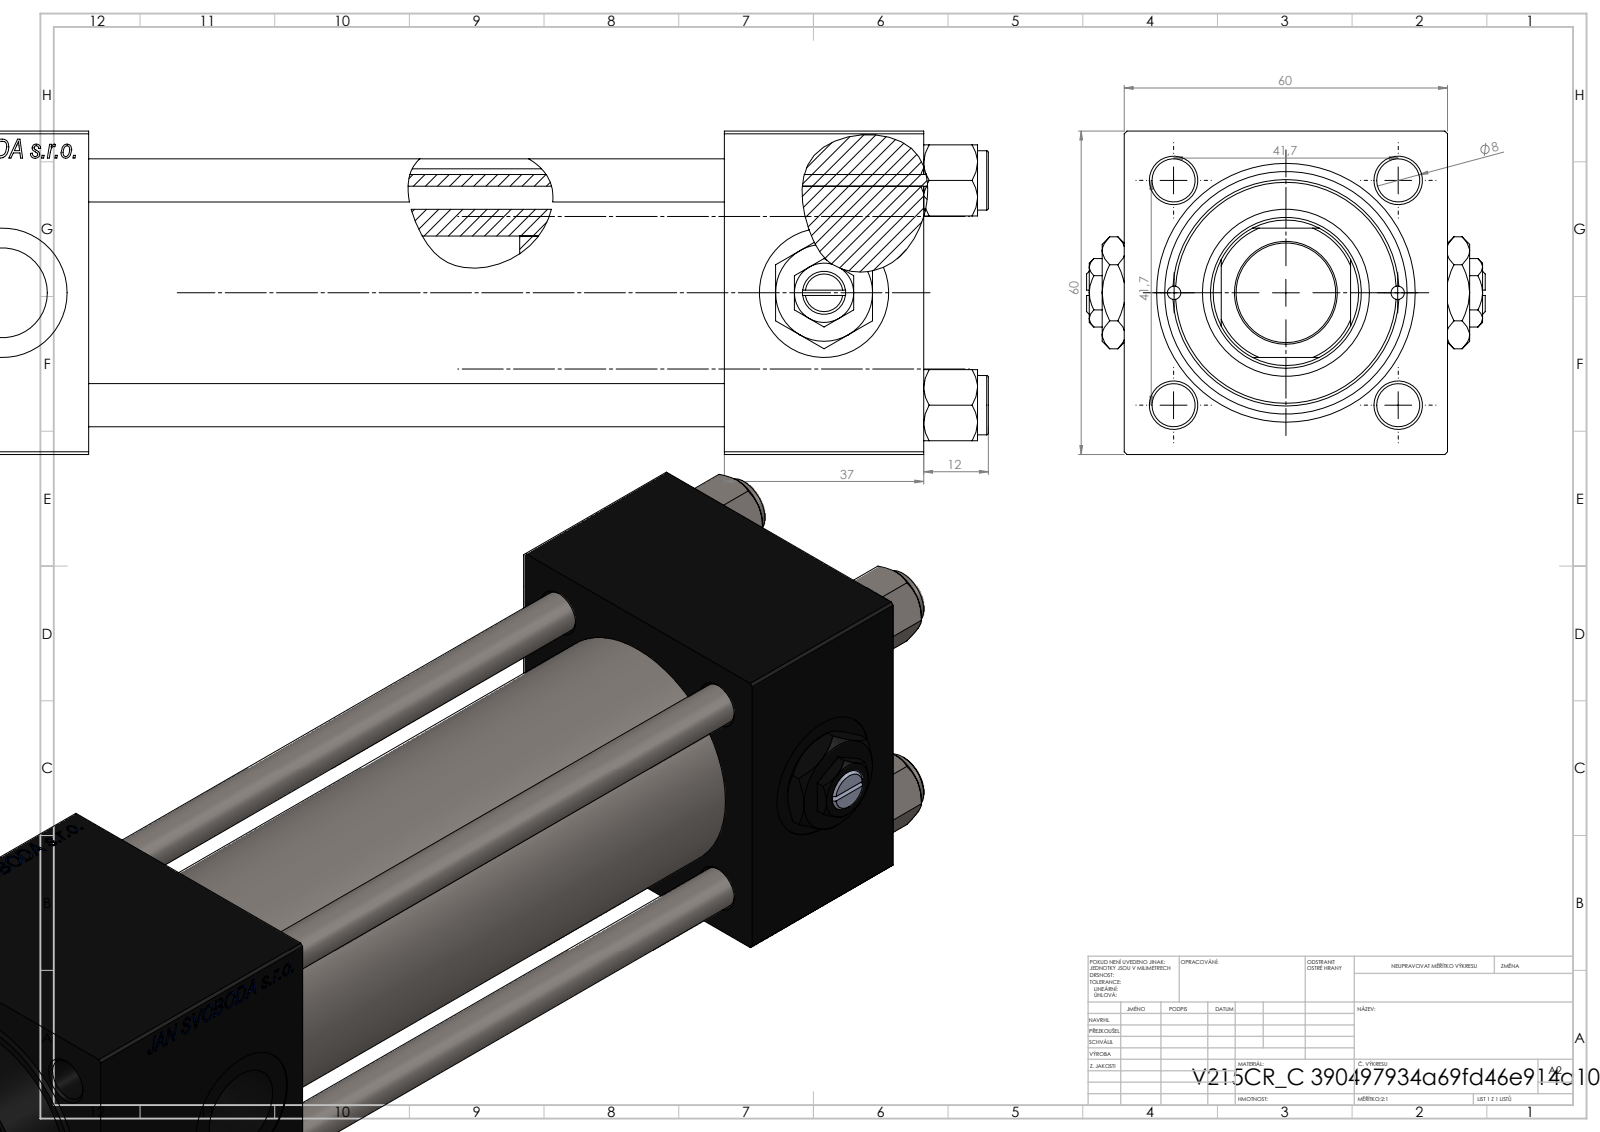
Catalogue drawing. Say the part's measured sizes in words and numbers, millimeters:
The part is named "V215_VC_A; V215CR_C_Body; V215CR_VCP_C; NUT_M5_C (+2 more)". Its 3-D file was written by "SolidWorks 2019 (CONFIG_CONTROL_DESIGN)". It is 13 solids with 1256 faces: 576 planar, 102 cylindrical and 578 other. Overall it measures 245 by 74 by 60 millimeters. Its volume is 494 140 cubic millimeters and its surface area 141 996 square millimeters. Round holes: 4 of diameter 8, 2 of diameter 2.5, 2 of diameter 7, 2 of diameter 16.66, 2 of diameter 24, 1 of diameter 18.5, 1 of diameter 28, 1 of diameter 31, 1 of diameter 40, 1 of diameter 45. Round bosses or shafts: 4 of diameter 11, 1 of diameter 46, 1 of diameter 42. Partial cylindrical surfaces (rounded edges, fillets, slot ends): 1 of radius 13.5. The main face-to-face distances are 60, 37, 155, 118, 53, 179.3, 142.3, 24.3, 208, 171. The hole center spacings are 20.85, 29.49, 41.7, 46.53, 20.75, 58.97, 41.5, 152.5.
